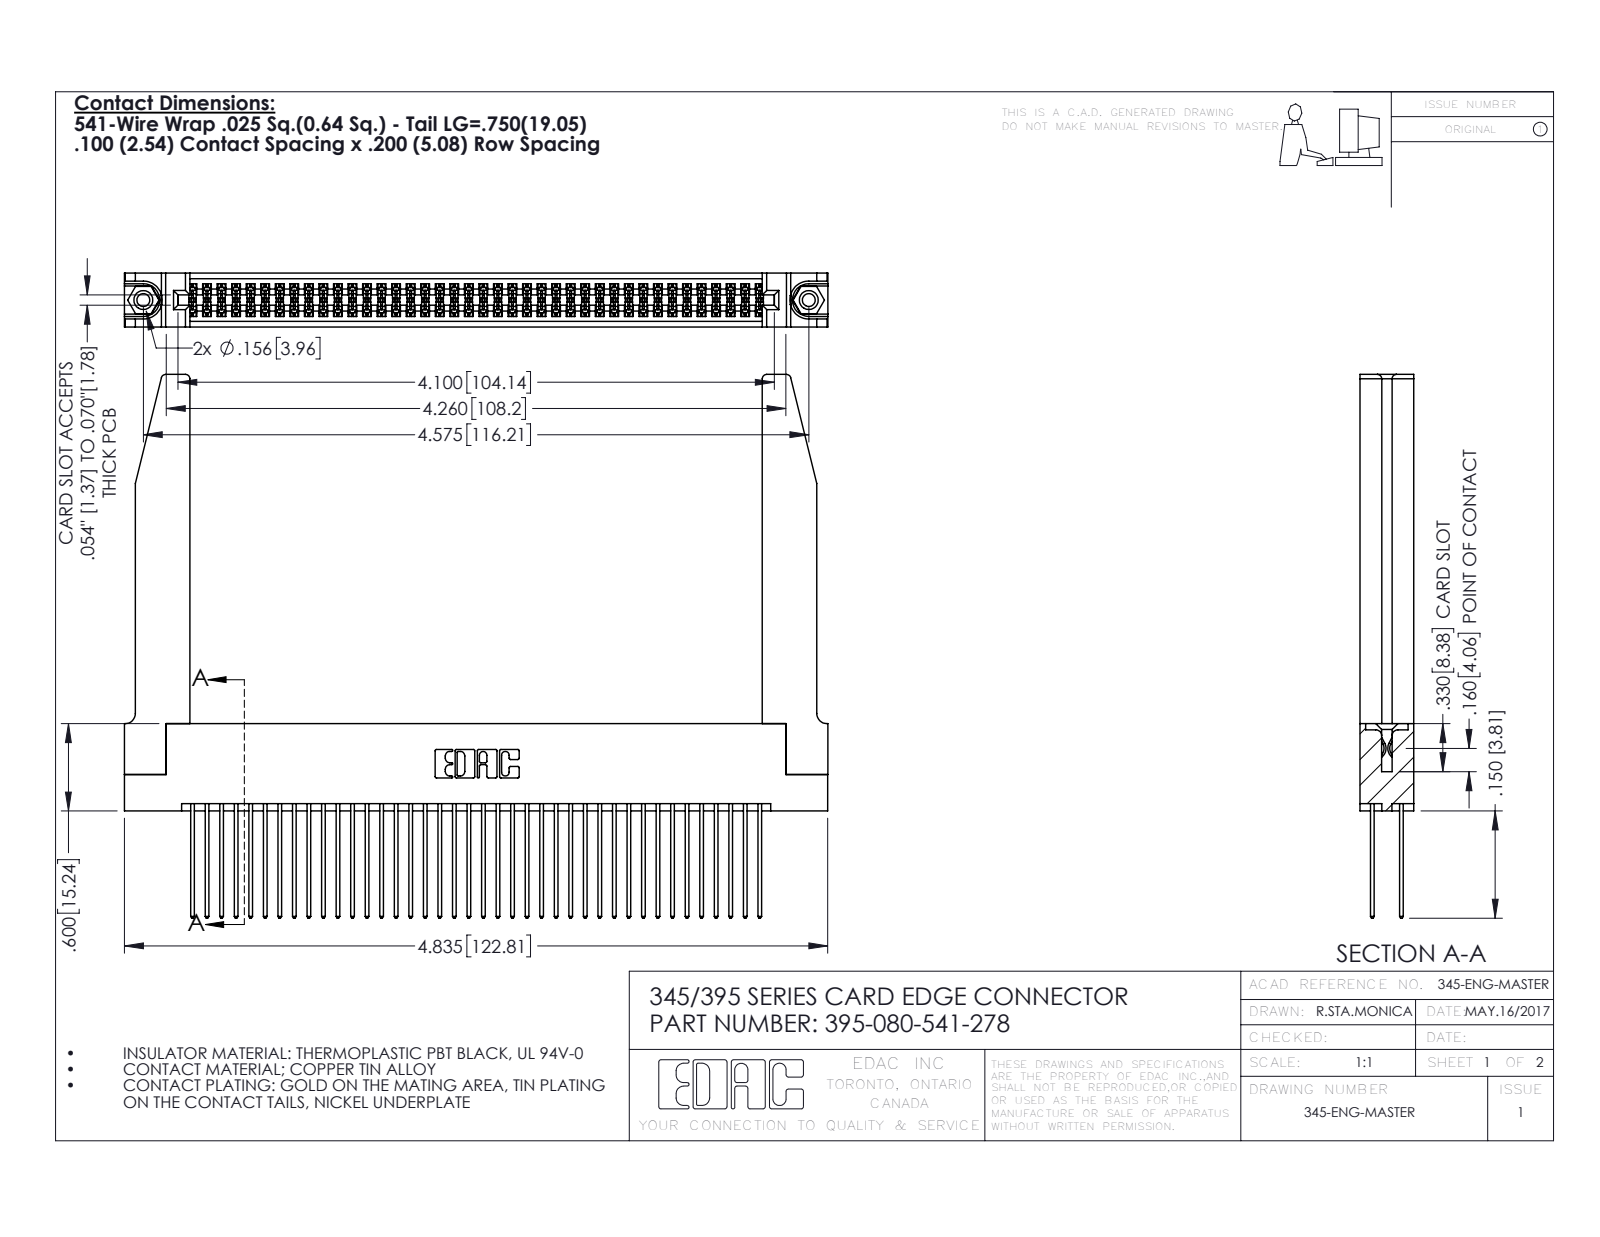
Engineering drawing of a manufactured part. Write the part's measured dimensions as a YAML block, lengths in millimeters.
part_name: "345-250-001_345-250-001-102; 345-292-001_345-293-141; 395-080-541-278; 345-220-078_345-220-078 (+1 more)"
step_written_by: "SolidWorks 2016 (CONFIG_CONTROL_DESIGN)"
units: millimeters
bodies: {solids: 85, faces: 4360, planar: 2862, cylindrical: 1446, other: 52}
overall_size: [122.8, 94.9, 9.4]
volume: 20140
surface_area: 27250
round_holes:
  - {diameter: 2.3, count: 2}
  - {diameter: 3.2, count: 2}
  - {diameter: 4, count: 2}
  - {diameter: 1.6, count: 1}
round_bosses_or_shafts:
  - {diameter: 3.9, count: 2}
partial_cylinders:
  - {radius: 0.2, count: 120}
  - {radius: 0.3, count: 80}
  - {radius: 0.3, count: 22}
  - {radius: 0.8, count: 8}
  - {radius: 0.2, count: 6}
  - {radius: 0.8, count: 6}
  - {radius: 0.7, count: 3}
  - {radius: 0.4, count: 2}
face_to_face_distances: [1.8, 7.6, 9.4, 5.1, 2.5, 6.9, 0.6, 5.7, 4.4, 3.8]
hole_center_spacings: [6.9, 110.2, 116.2]
